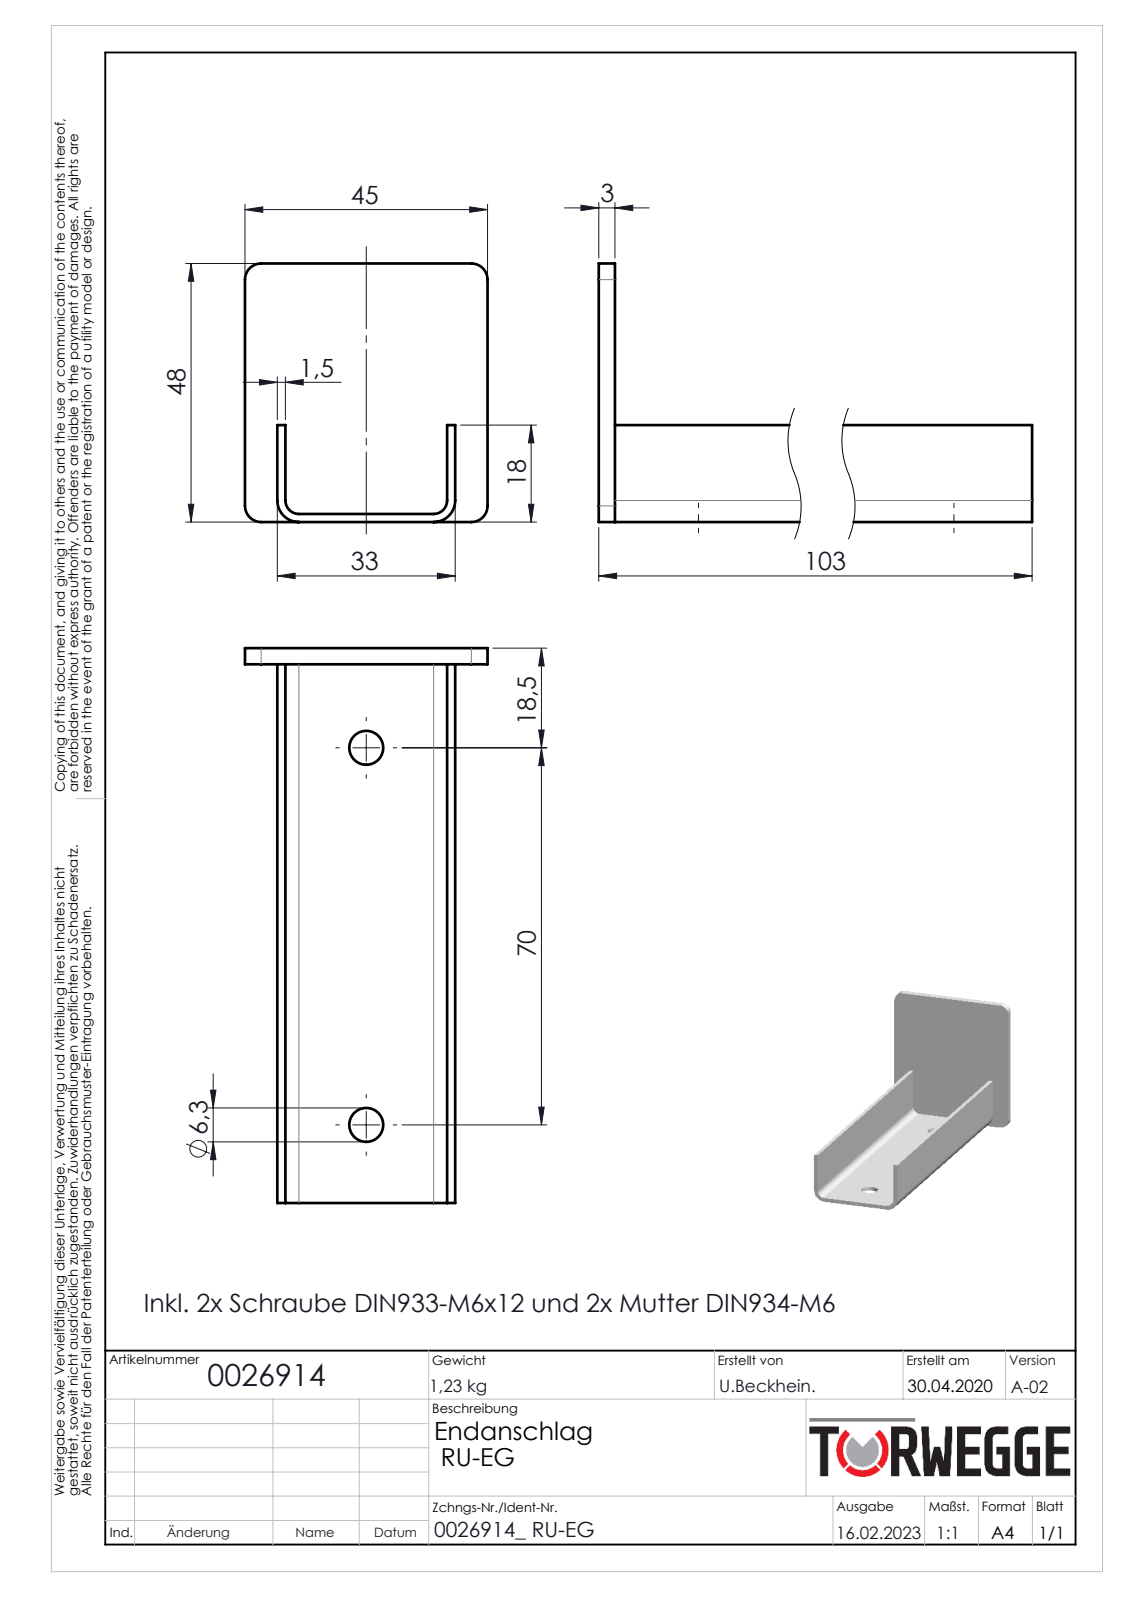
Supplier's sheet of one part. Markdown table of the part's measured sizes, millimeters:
| quantity | value |
| --- | --- |
| part name | 0026914 |
| STEP written by | SolidWorks 2018 (AUTOMOTIVE_DESIGN) |
| units | millimeters |
| bodies | 2 solids, 28 faces (16 planar, 12 cylindrical, 0 other) |
| overall size | 103 × 48 × 45 |
| volume | 15 845 mm³ |
| surface area | 17 913 mm² |
| round holes (diameter × count) | 6.3 × 2 |
| partial cylindrical surfaces (radius × count) | 3 × 4, 2.5 × 2, 4 × 2 |
| main face-to-face distances | 1.5, 31.5, 3, 30, 33, 18, 16.5, 6, 7.5, 37.5 |
| hole center spacings | 70 |
